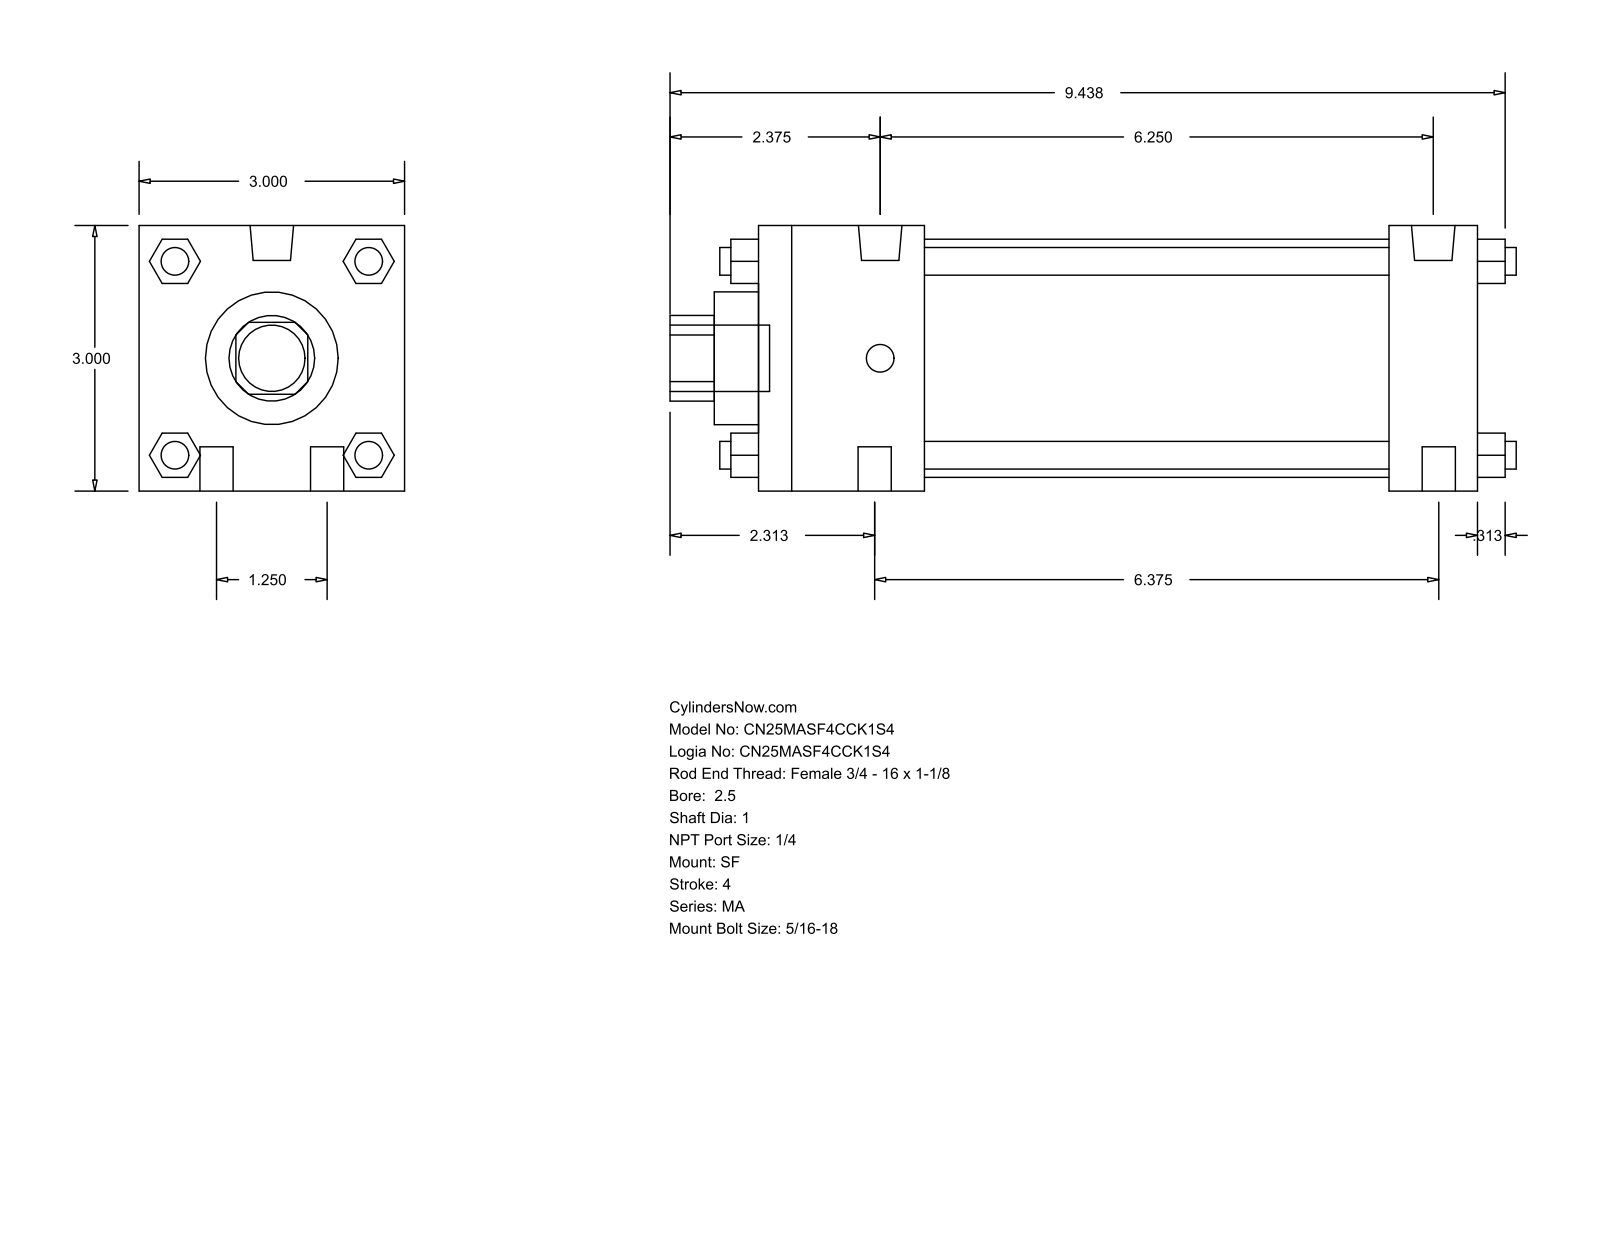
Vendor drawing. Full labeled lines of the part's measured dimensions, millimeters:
Part name (STEP PRODUCT): MA_SF__0250_1
STEP written by: GSSL Pune (CONFIG_CONTROL_DESIGN)
Units: millimetres
Bodies: 0 solids, 124 faces (94 planar, 30 cylindrical, 0 other)
Overall size (bounding box): 242.89 × 76.2 × 76.2
Round holes (diameter × count): ⌀25.4 ×1, ⌀38.1 ×1, ⌀68.33 ×1
Round bosses / shafts (diameter × count): ⌀7.94 ×6, ⌀9.53 ×4, ⌀12.49 ×2, ⌀19.05 ×1
Partial cylindrical surfaces — rounded edges, fillets, slot ends (radius × count): R12.29 ×1
Main face-to-face distances: 76.2, 206.38, 12.7, 25.4, 180.98, 47.63, 133.35, 158.75, 27.81, 48.17
